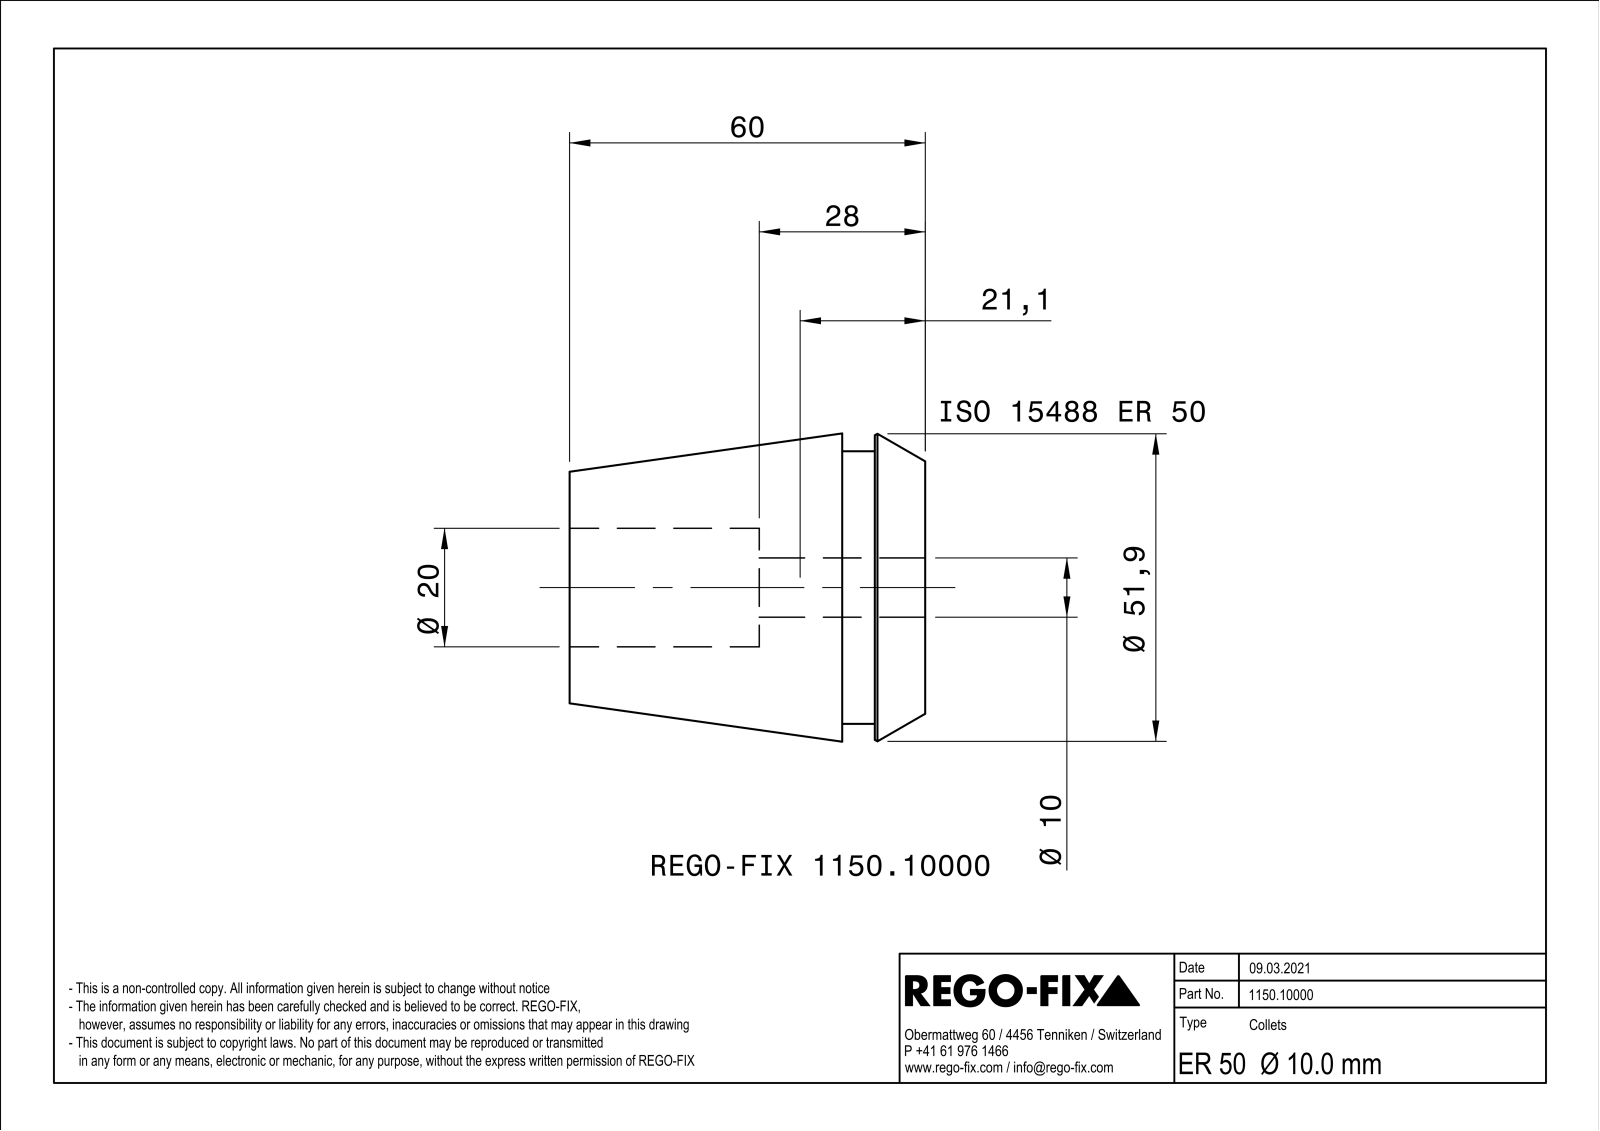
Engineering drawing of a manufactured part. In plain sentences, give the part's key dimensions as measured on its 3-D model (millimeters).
The part is named "NOCUT". Its 3-D file was written by "SIEMENS PLM Software Solid Edge ST10 (AUTOMOTIVE_DESIGN)". It is 1 solid with 288 faces: 120 planar, 32 cylindrical and 136 other. Overall it measures 60 by 51.99 by 51.99 millimeters. Its volume is 75 197 cubic millimeters and its surface area 37 777 square millimeters. Round holes: 1 of diameter 20. Round bosses or shafts: 1 of diameter 46. Partial cylindrical surfaces (rounded edges, fillets, slot ends): 1 of radius 5. The main face-to-face distances are 1, 1.02, 0.98, 60, 14, 46, 8.5, 5.5, 51.5, 28.
